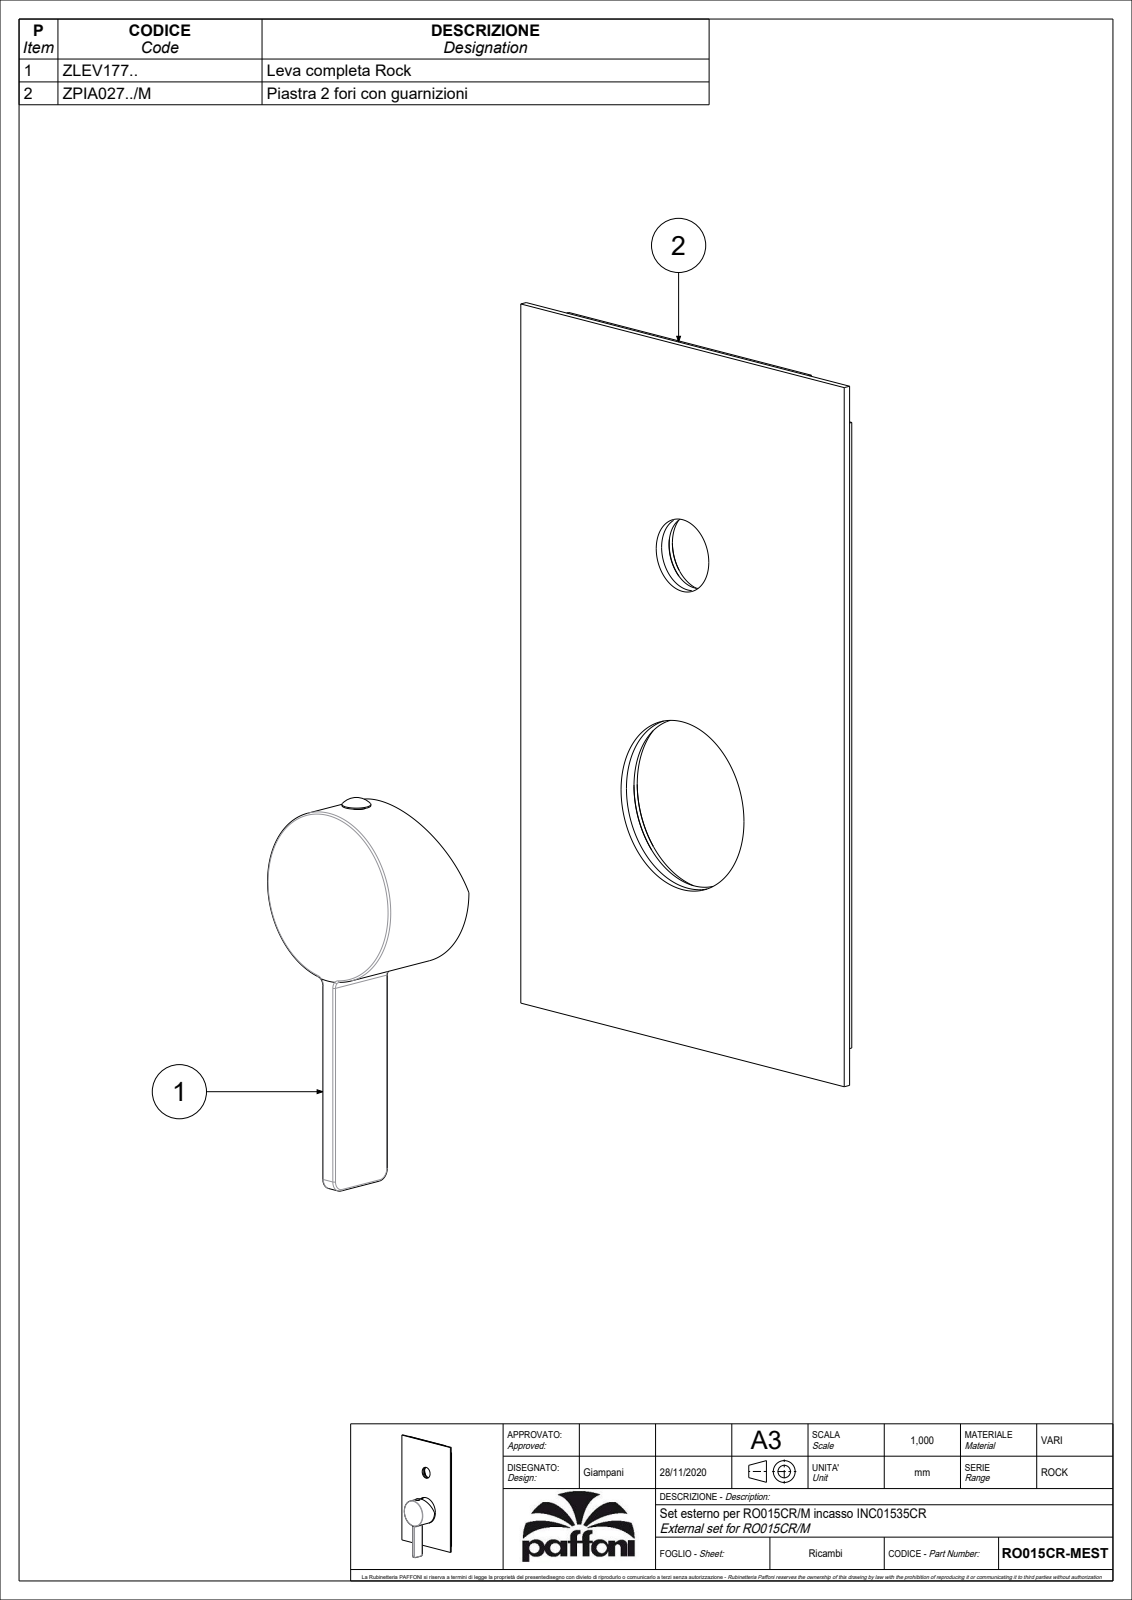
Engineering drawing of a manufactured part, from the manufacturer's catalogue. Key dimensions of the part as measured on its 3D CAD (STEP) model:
Part name (STEP PRODUCT): RO015CR-MEST
STEP written by: CREO PARAMETRIC BY PTC INC, 2020044 (CONFIG_CONTROL_DESIGN)
Units: millimetres
Bodies: 2 solids, 180 faces (73 planar, 55 cylindrical, 52 other)
Overall size (bounding box): 205 × 120 × 39.5
Volume: 69 603 mm³ · Surface area: 62 935 mm²
Round holes (diameter × count): ⌀3 ×1, ⌀19.5 ×1, ⌀21.5 ×1, ⌀25 ×1, ⌀45.6 ×1, ⌀47.6 ×1, ⌀51.1 ×1
Round bosses / shafts (diameter × count): ⌀54.6 ×1, ⌀45.5 ×1, ⌀28.5 ×1, ⌀7.6 ×1, ⌀5.5 ×1, ⌀5 ×1
Partial cylindrical surfaces — rounded edges, fillets, slot ends (radius × count): R0.5 ×9, R0.3 ×2, R1.5 ×2, R2 ×2, R3 ×2, R3.5 ×1
Main face-to-face distances: 2, 0.8, 2.8, 4.5, 57.75, 62.25, 30.8, 30, 28, 5.5
Hole centre spacings: 68
